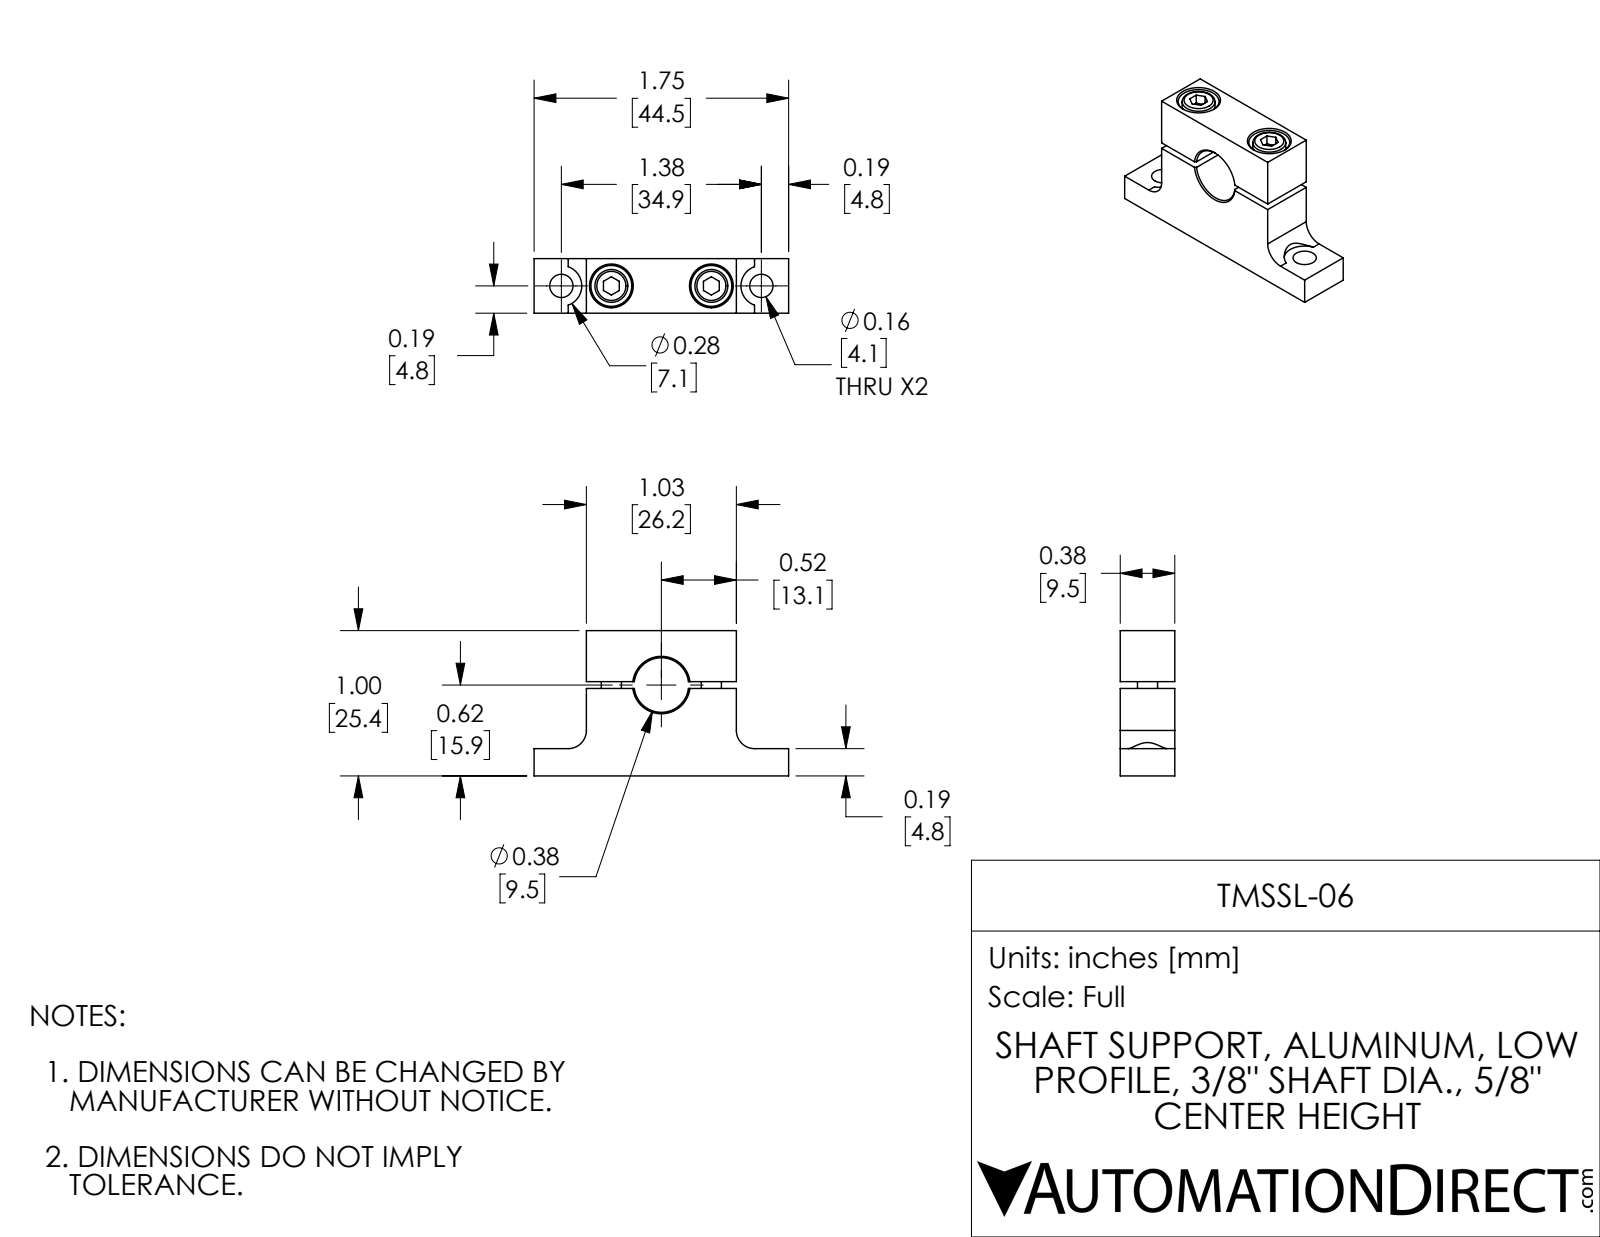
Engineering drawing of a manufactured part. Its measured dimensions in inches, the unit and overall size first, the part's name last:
Units: inches
Overall size (bounding box): 1.75 × 0.999 × 0.375
Round holes (diameter × count): ⌀0.104 ×2, ⌀0.15 ×2, ⌀0.16 ×2, ⌀0.281 ×2
Round bosses / shafts (diameter × count): ⌀0.226 ×2, ⌀0.138 ×2
Partial cylindrical surfaces — rounded edges, fillets, slot ends (radius × count): R0.125 ×2, R0.141 ×2, R0.187 ×1, R0.188 ×1
Main face-to-face distances: 0.375, 0.998, 0.601, 0.398, 1.031, 0.648, 0.047, 0.35, 0.187, 0.413
Hole centre spacings: 0.344, 1.031, 0.687, 1.375
Volume: 0.368 in³ · Surface area: 6.598 in²
Bodies: 4 solids, 92 faces (38 planar, 30 cylindrical, 24 other)
Part name (STEP PRODUCT): TMSSL-06
STEP written by: SolidWorks 2017 (AUTOMOTIVE_DESIGN)
